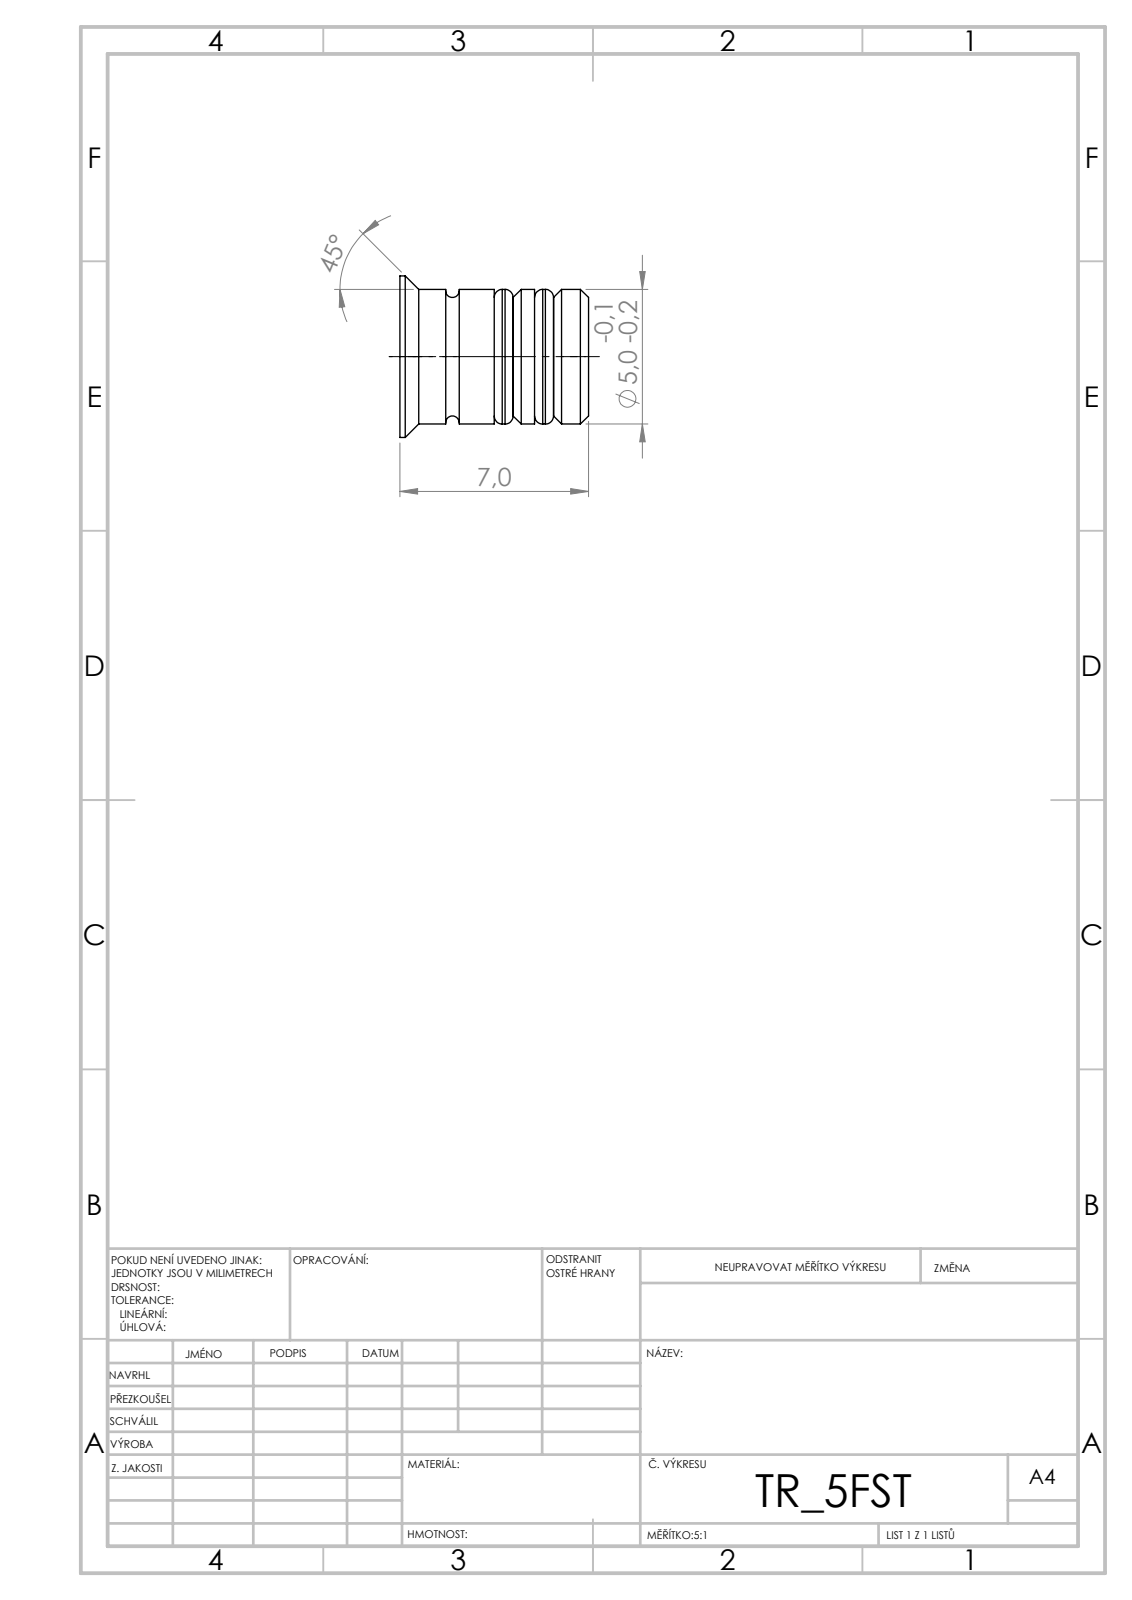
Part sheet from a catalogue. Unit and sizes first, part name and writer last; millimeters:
Units: millimetres
Overall size (bounding box): 7 × 6 × 6
Round bosses / shafts (diameter × count): ⌀6 ×1, ⌀5 ×1, ⌀4.4 ×1, ⌀2 ×1
Main face-to-face distances: 3.5, 1.5, 0.7, 5, 2, 2.2, 1.3, 2.8, 5.7, 0.8
Volume: 152 mm³ · Surface area: 286 mm²
Bodies: 3 solids, 67 faces (25 planar, 20 cylindrical, 22 other)
STEP written by: SolidWorks 2019 (CONFIG_CONTROL_DESIGN)
